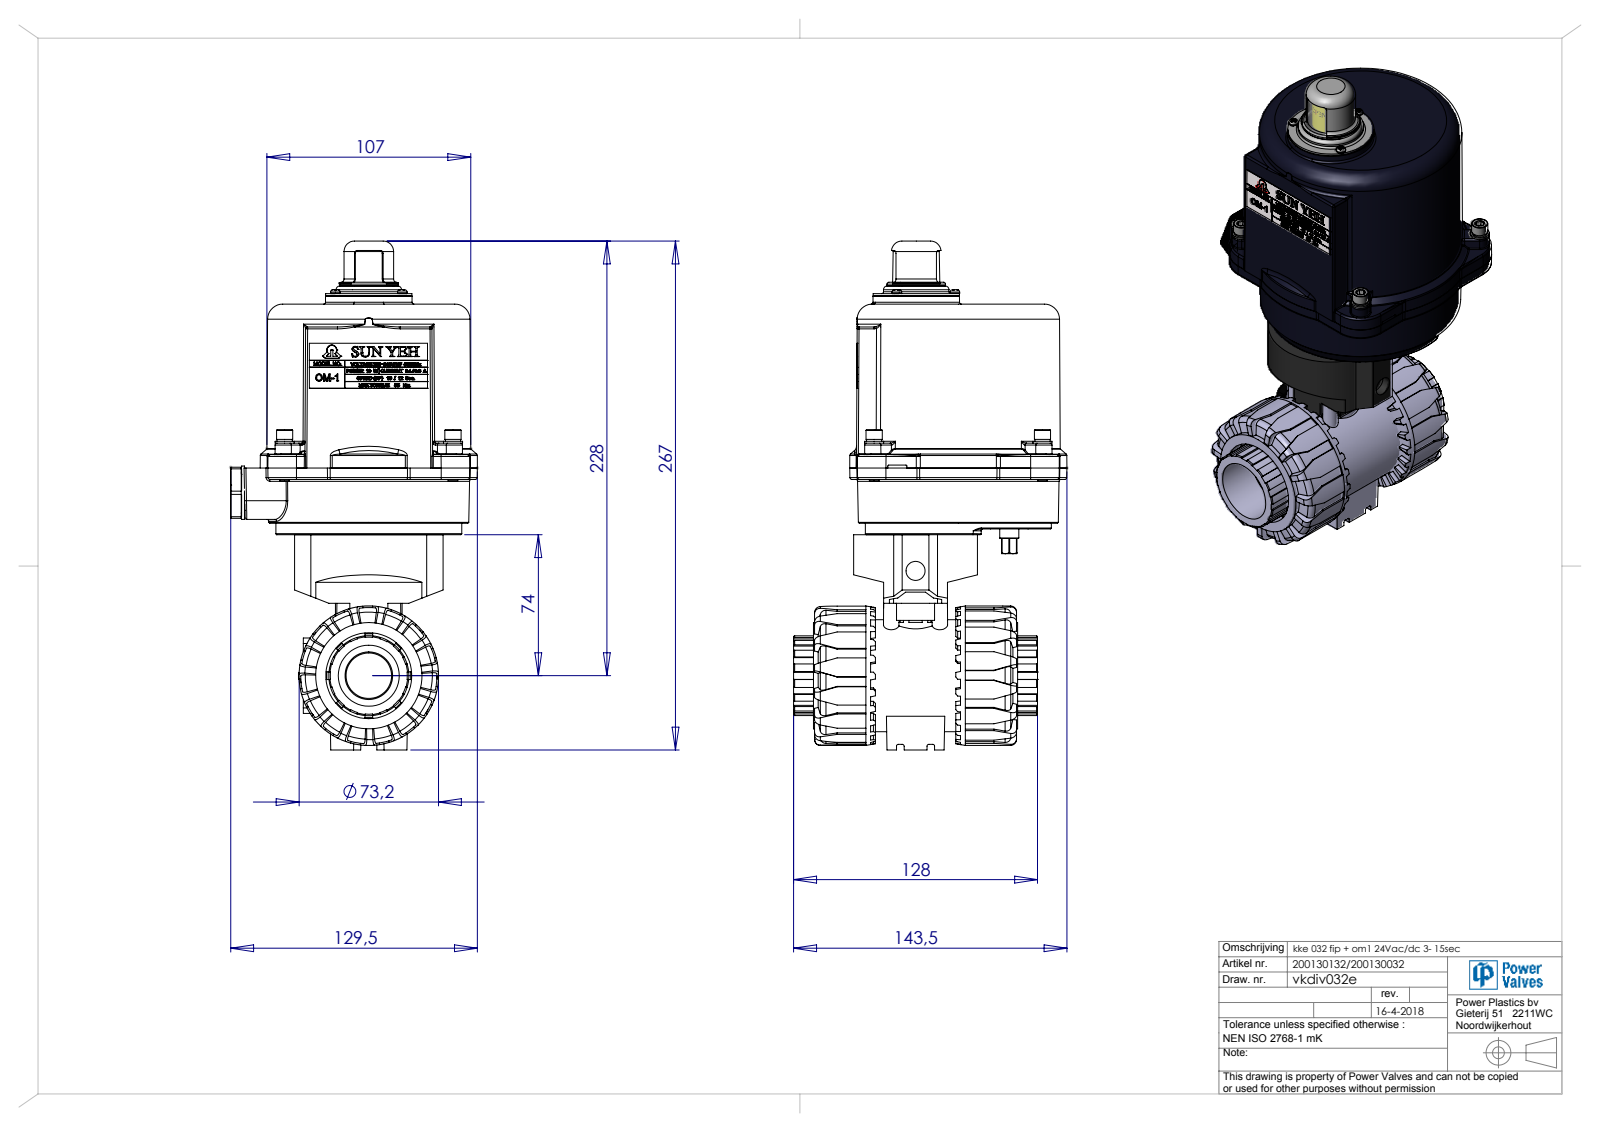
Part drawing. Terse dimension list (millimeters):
name: vkdiv032e_06; vkdiv032e_04; Fip adapter; vkdiv032e (+8 more)
written by: SolidWorks 2014 (AUTOMOTIVE_DESIGN)
unit: mm
bodies: 28 solids, 5243 faces (2332 planar, 1035 cylindrical, 1876 other)
size: 267.1 × 143.46 × 129.47
volume: 731 075 mm³; area: 288 560 mm²
holes: 8× ⌀5, 7× ⌀3.5, 6× ⌀2.9, 6× ⌀5.5, 4× ⌀3.24, 4× ⌀4.13, 4× ⌀4.2, 4× ⌀4.6, 4× ⌀6.5, 2× ⌀2.46, 2× ⌀2.46, 2× ⌀4
bosses: 8× ⌀5, 5× ⌀10, 5× ⌀8, 4× ⌀8.5, 4× ⌀4.4, 3× ⌀28, 3× ⌀3, 2× ⌀21
rounds: 69× R1, 33× R1.5, 28× R0.24, 28× R3.1, 14× R0.5, 10× R0.1, 8× R1.35, 6× R0.33
face distances: 7, 35, 118.5, 83.5, 2.5, 121, 6, 3, 86, 78
hole spacings: 25.46, 25, 13.02, 26.05, 7, 18, 0.36, 6.75
